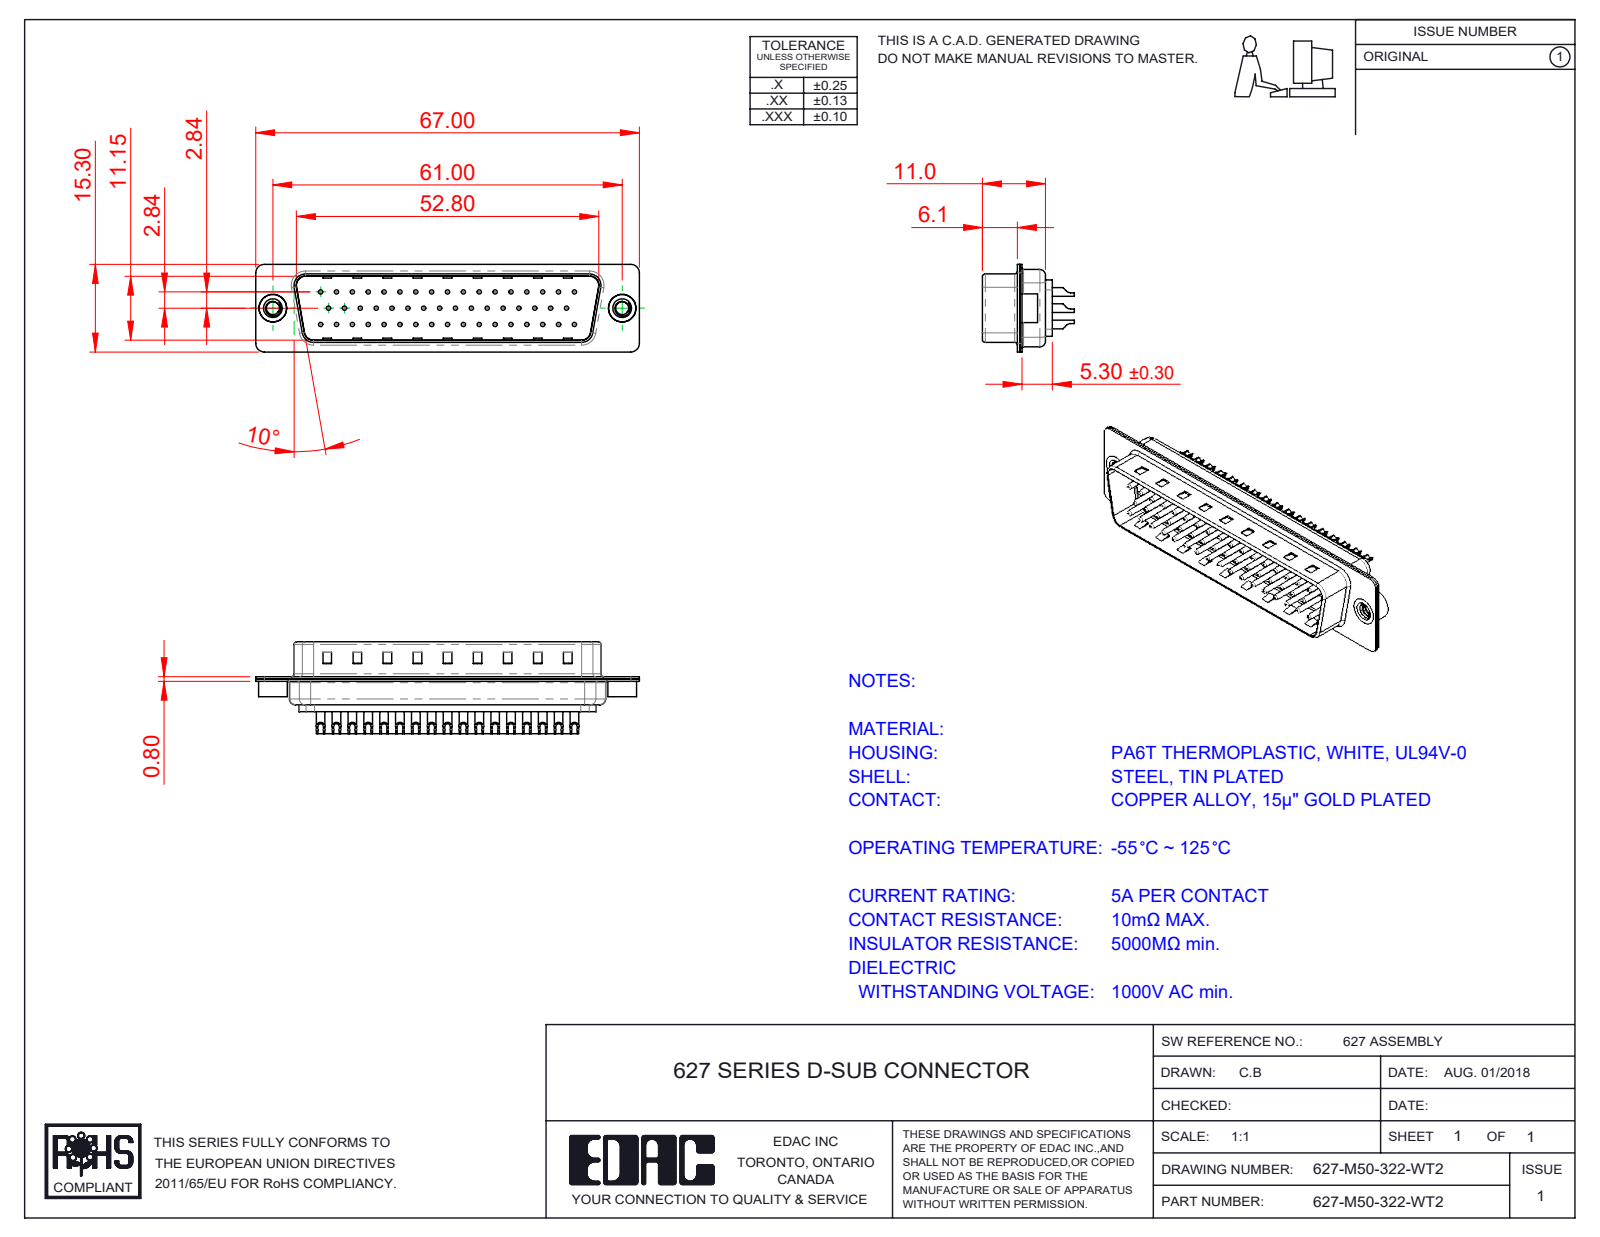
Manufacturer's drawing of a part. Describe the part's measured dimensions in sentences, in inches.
The part is named "627M Shell Rear_50 Contacts; 627M Contact Row 1_22; 627M Housing_50 Contacts; 627M Contact Row 3_22 (+4 more)". Its 3-D file was written by "SolidWorks 2020 (CONFIG_CONTROL_DESIGN)". It is 55 solids with 2262 faces: 653 planar, 941 cylindrical and 668 other. Overall it measures 2.638 by 0.632 by 0.602 inches. Its volume is 0.283 cubic inches and its surface area 17.31 square inches. Round holes: 50 of diameter 0.03, 50 of diameter 0.039, 50 of diameter 0.063, 50 of diameter 0.079, 2 of diameter 0.089, 2 of diameter 0.157, 2 of diameter 0.189. Round bosses or shafts: 50 of diameter 0.059, 2 of diameter 0.197, 2 of diameter 0.193. Partial cylindrical surfaces (rounded edges, fillets, slot ends): 16 of radius 0.059, 12 of radius 0.079, 8 of radius 0.02, 8 of radius 0.063, 7 of radius 0.039, 4 of radius 0.01, 4 of radius 0.024, 4 of radius 0.026. The main face-to-face distances are 0.016, 0.455, 0.224, 0.24, 0.031, 0.03, 0.485, 0.485, 0.516, 0.209. The hole center spacings are 0.124, 0.109, 0.218, 0.327, 0.436, 0.545, 0.654, 0.198.
